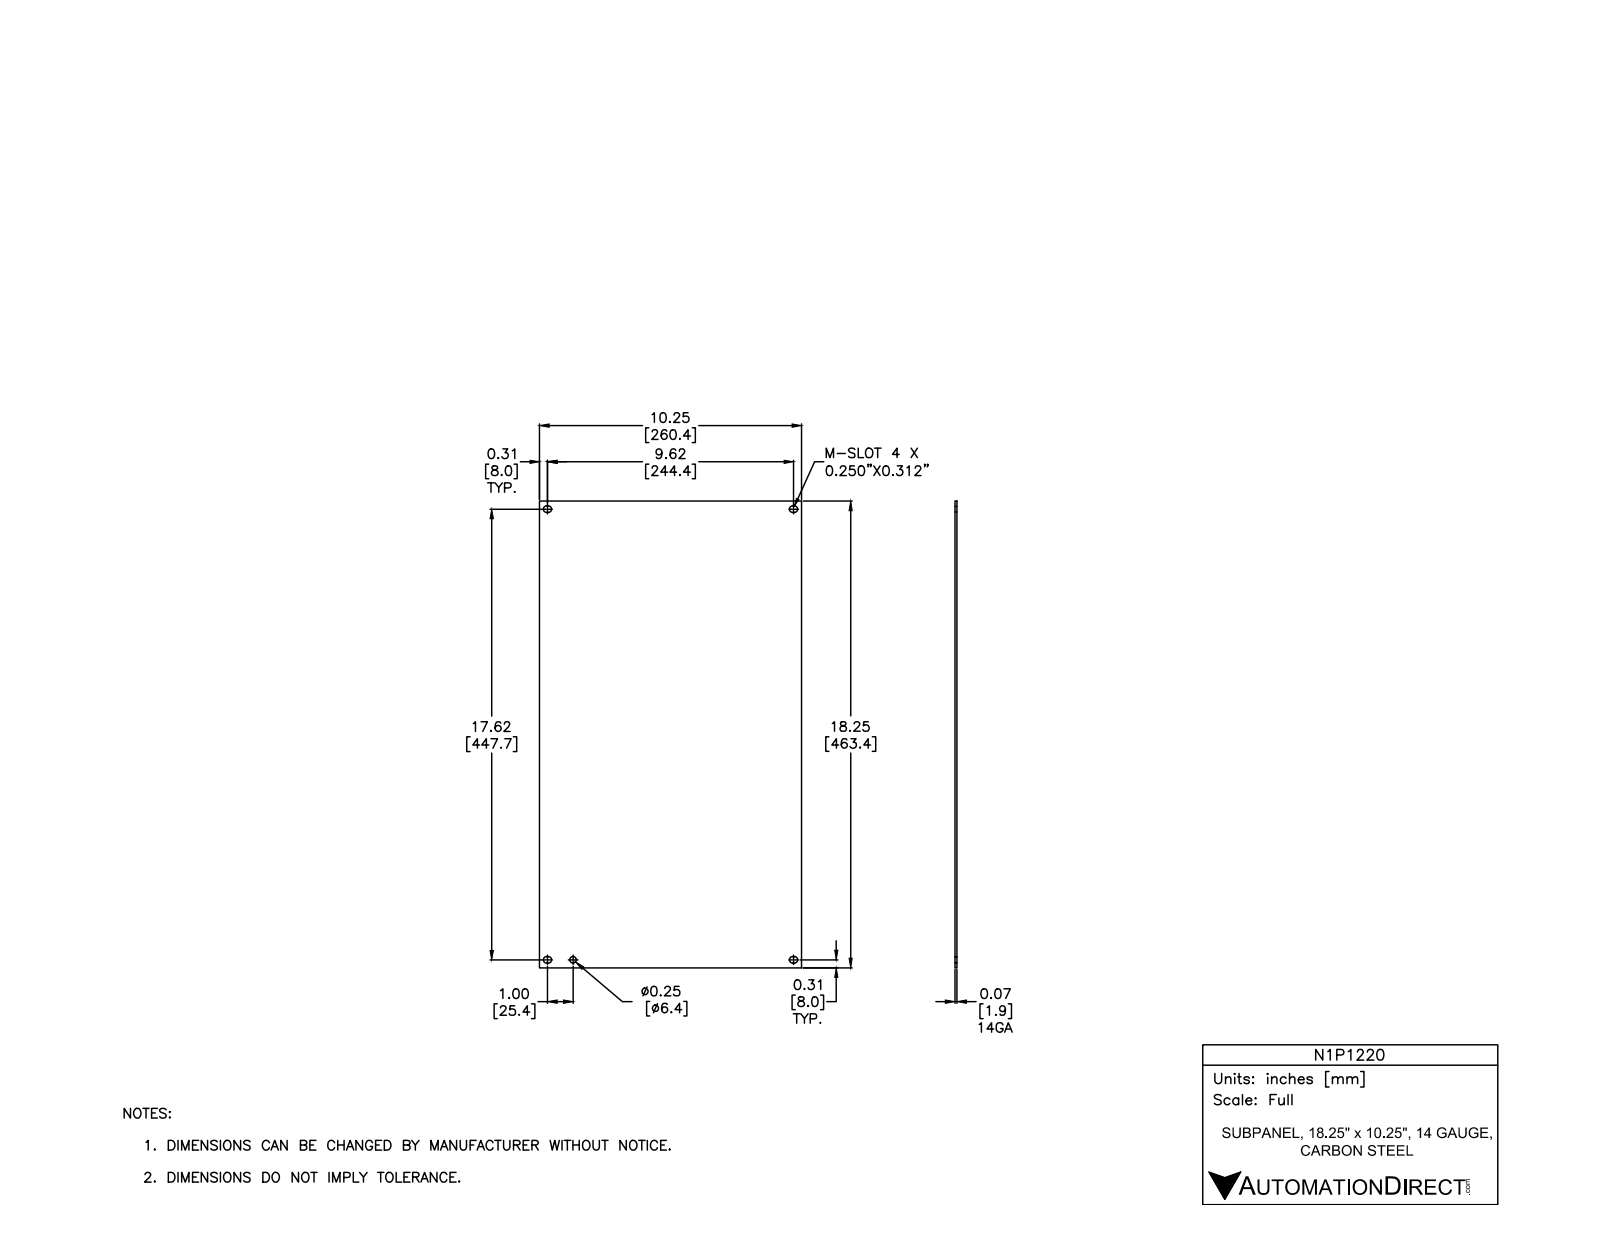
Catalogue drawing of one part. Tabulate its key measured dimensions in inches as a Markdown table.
| quantity | value |
| --- | --- |
| part name | N1P1220 |
| STEP written by | Autodesk Inventor 2012 (AUTOMOTIVE_DESIGN) |
| units | inches |
| bodies | 1 solid, 23 faces (14 planar, 9 cylindrical, 0 other) |
| overall size | 18.25 × 10.25 × 0.074 |
| volume | 13.82 in³ |
| surface area | 378.1 in² |
| round holes (diameter × count) | 0.25 × 1 |
| partial cylindrical surfaces (radius × count) | 0.125 × 8 |
| main face-to-face distances | 0.074, 10.25, 18.25, 0.438, 17.812, 0.188, 18.062, 0.25, 17.624, 17.374 |
